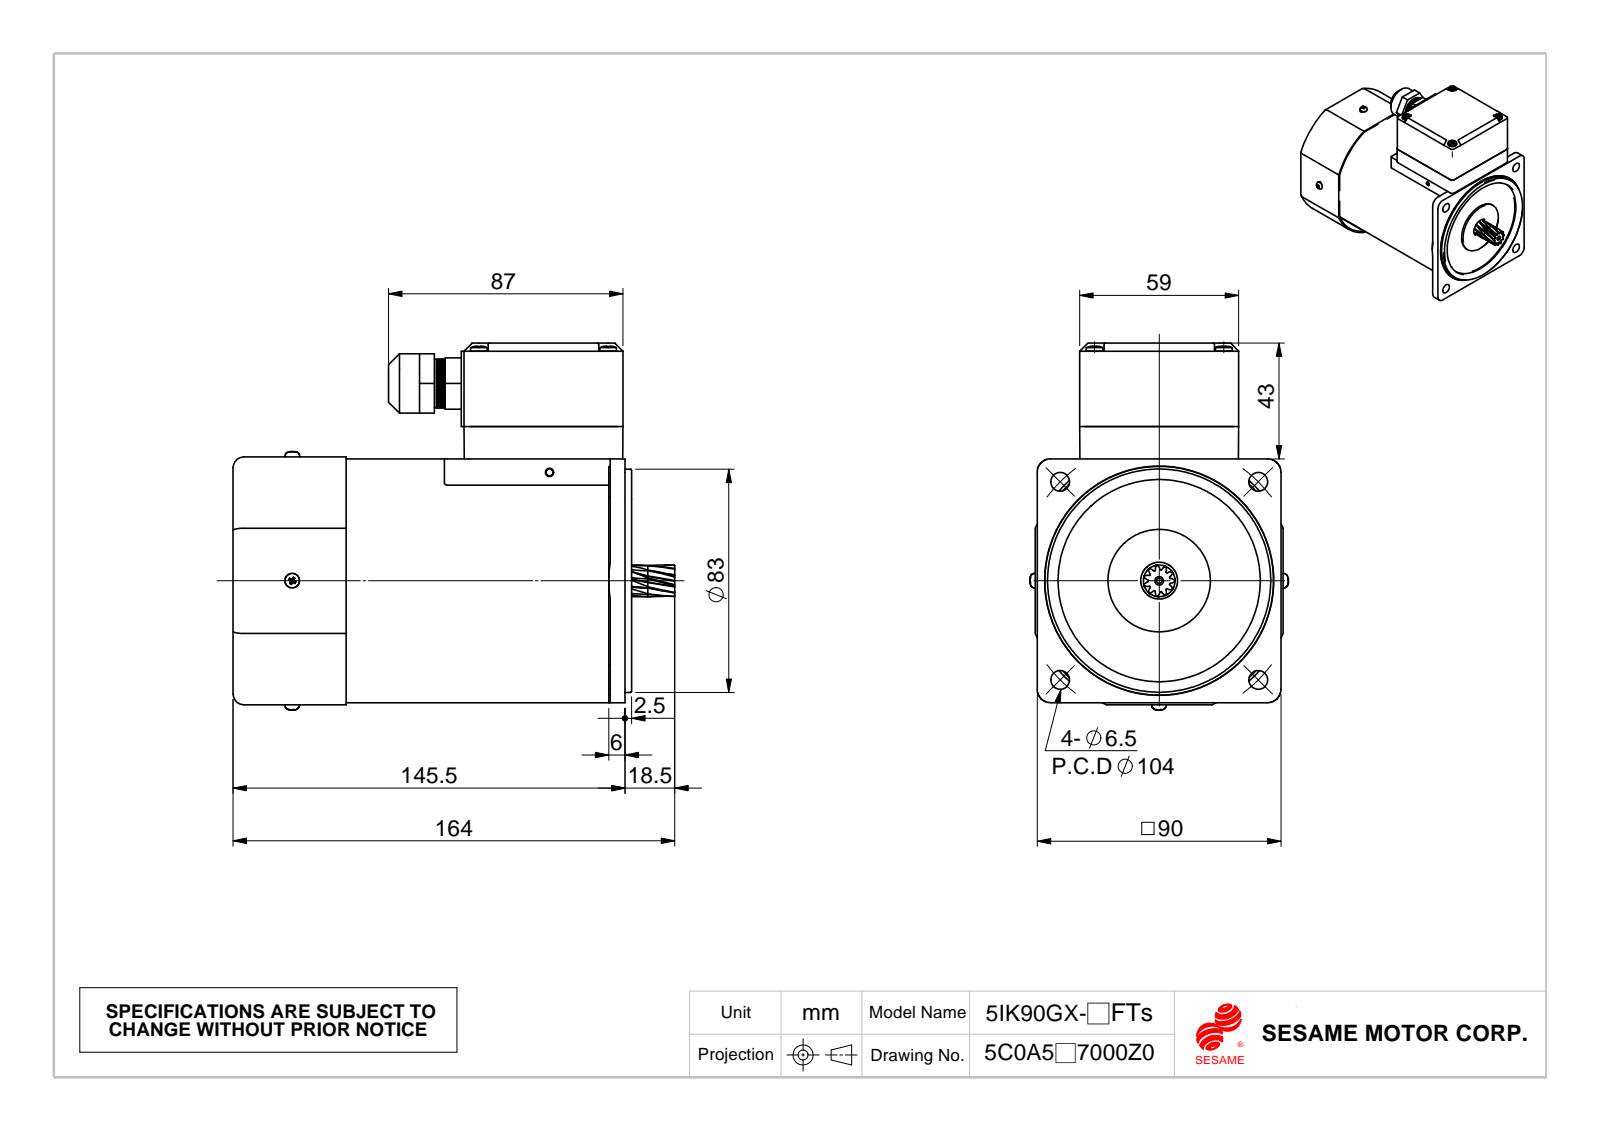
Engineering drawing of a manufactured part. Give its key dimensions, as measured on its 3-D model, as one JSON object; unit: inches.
{"part_name": "風扇蓋FC-9042-21; Ts下墊片; M590Ts-F; 成品180度 (+1 more)", "step_written_by": "SolidWorks 2010 (CONFIG_CONTROL_DESIGN)", "units": "inches", "bodies": {"solids": 16, "faces": 2770, "planar": 331, "cylindrical": 944, "other": 1495}, "overall_size": [6.457, 5.363, 3.776], "volume_in3": 62.98, "surface_area_in2": 229.8, "round_holes": [[0.13, 4], [0.138, 4], [0.154, 4], [0.169, 4], [0.276, 4], [0.098, 3], [0.079, 1], [0.256, 1], [0.433, 1], [0.472, 1], [0.539, 1], [0.571, 1]], "round_bosses_or_shafts": [[0.118, 6], [0.248, 4], [0.433, 3], [0.217, 2], [3.563, 1], [3.386, 1], [3.346, 1], [3.307, 1]], "partial_cylinders_radius": [[0.012, 16], [0.079, 16], [0.039, 10], [0.157, 10], [0.02, 8], [0.118, 8], [0.059, 4], [0.069, 4]], "face_to_face_distances": [0.039, 0.472, 0.03, 3.583, 0.154, 0.63, 5.472, 5.626, 5.512, 5.665], "hole_center_spacings": [1.89, 2.047, 2.895, 0.459, 0.486, 0.5, 0.981, 0.984]}
